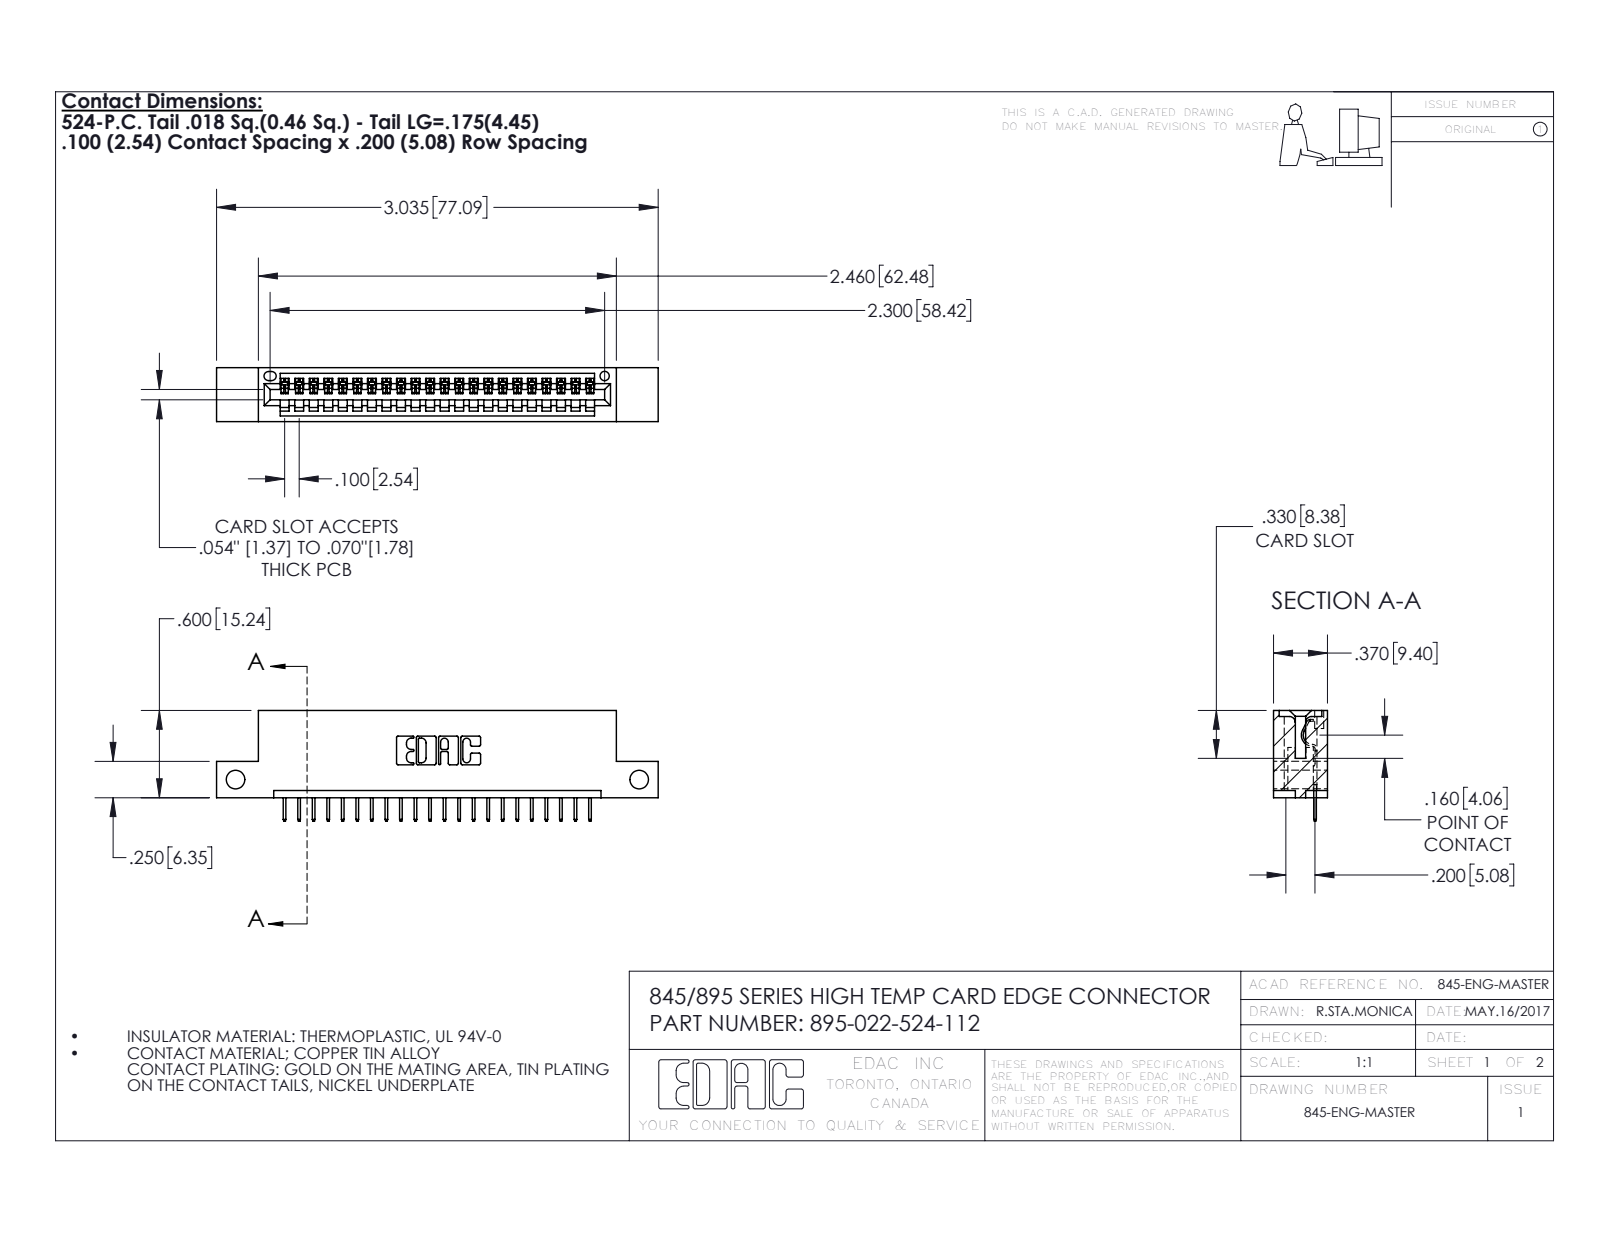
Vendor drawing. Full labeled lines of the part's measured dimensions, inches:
Part name (STEP PRODUCT): 395-022-524-112; 345 Part_Flush Mounting Lugs - Side Mount; 345-292-001_345-293-124
STEP written by: SolidWorks 2016 (CONFIG_CONTROL_DESIGN)
Units: inches
Bodies: 23 solids, 1490 faces (1092 planar, 398 cylindrical, 0 other)
Overall size (bounding box): 3.035 × 0.762 × 0.37
Volume: 0.426 in³ · Surface area: 13.31 in²
Round holes (diameter × count): ⌀0.128 ×2, ⌀0.064 ×1
Partial cylindrical surfaces — rounded edges, fillets, slot ends (radius × count): R0.006 ×44, R0.01 ×22, R0.007 ×6, R0.031 ×6, R0.026 ×3, R0.031 ×2, R0.04 ×2, R0.014 ×1
Main face-to-face distances: 0.298, 0.072, 0.37, 0.2, 0.098, 0.272, 0.025, 0.225, 0.072, 0.149
Hole centre spacings: 2.775
